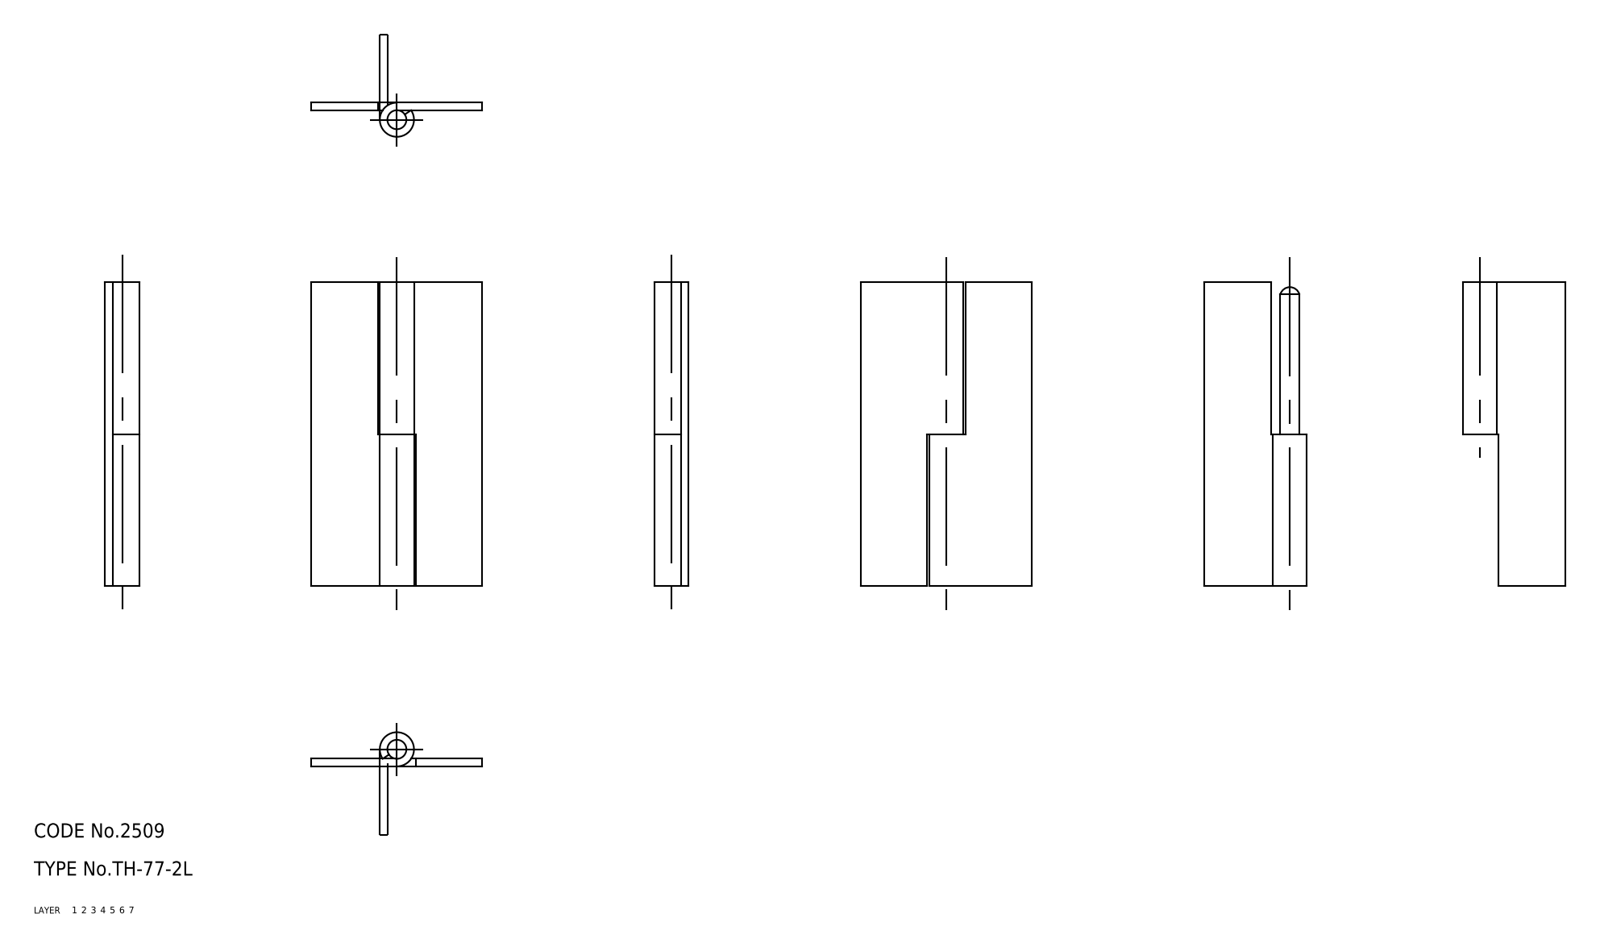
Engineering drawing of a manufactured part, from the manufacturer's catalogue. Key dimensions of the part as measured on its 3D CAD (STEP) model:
Part name (STEP PRODUCT): shaft; hinge piece_B; hinge piece_A; TH_77_2L_15995_36
STEP written by: CADfix (AUTOMOTIVE_DESIGN)
Units: millimetres
Bodies: 3 solids, 24 faces (0 planar, 0 cylindrical, 24 other)
Overall size (bounding box): 64 × 36 × 7.2
Volume: 5 578 mm³ · Surface area: 7 415 mm²
